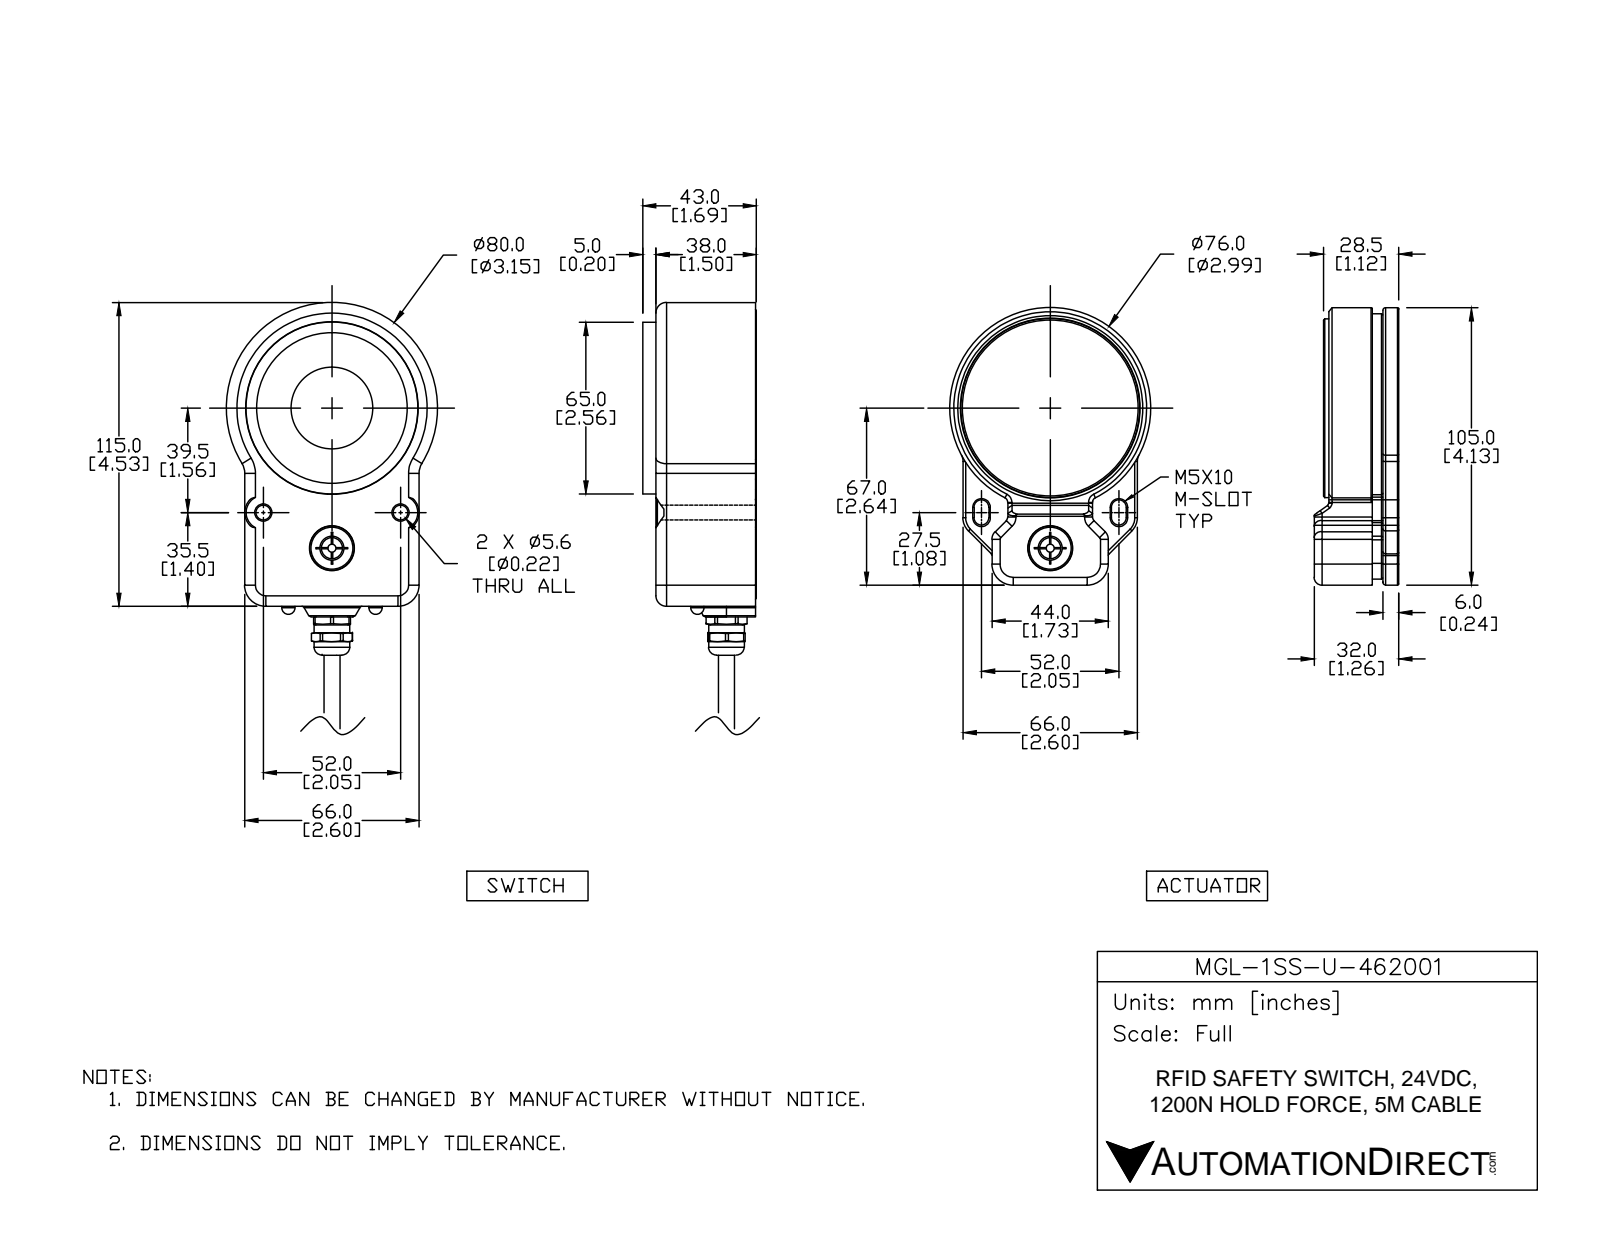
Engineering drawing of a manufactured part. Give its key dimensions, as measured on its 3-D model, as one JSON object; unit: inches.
{"part_name": "MGL-1SS-U-462001_1; MGL-1SS-U-462001; MGL-1SS-U-462001_2", "step_written_by": "SolidWorks 2017 (AUTOMOTIVE_DESIGN)", "units": "inches", "bodies": {"solids": 19, "faces": 1647, "planar": 423, "cylindrical": 679, "other": 545}, "overall_size": [8.465, 3.15, 2.854], "volume_in3": 19.52, "surface_area_in2": 219.9, "round_holes": [[0.098, 8], [0.13, 6], [0.197, 6], [0.453, 5], [0.157, 3], [0.315, 3], [0.354, 3], [0.22, 2], [0.276, 2], [0.252, 1], [0.266, 1], [0.268, 1]], "round_bosses_or_shafts": [[0.02, 4], [0.472, 2], [0.228, 2], [0.22, 2], [0.118, 2], [0.047, 2], [2.992, 1], [2.811, 1]], "partial_cylinders_radius": [[0.02, 188], [0.039, 64], [0.079, 26], [0.012, 17], [0.118, 13], [0.157, 12], [0.217, 10], [0.024, 7]], "face_to_face_distances": [0.236, 0.315, 0.098, 0.413, 1.378, 2.303, 1.122, 0.118, 0.354, 2.205], "hole_center_spacings": [1.392, 1.969, 0.984, 1.28, 1.537, 0.787, 1.364, 0.349]}
